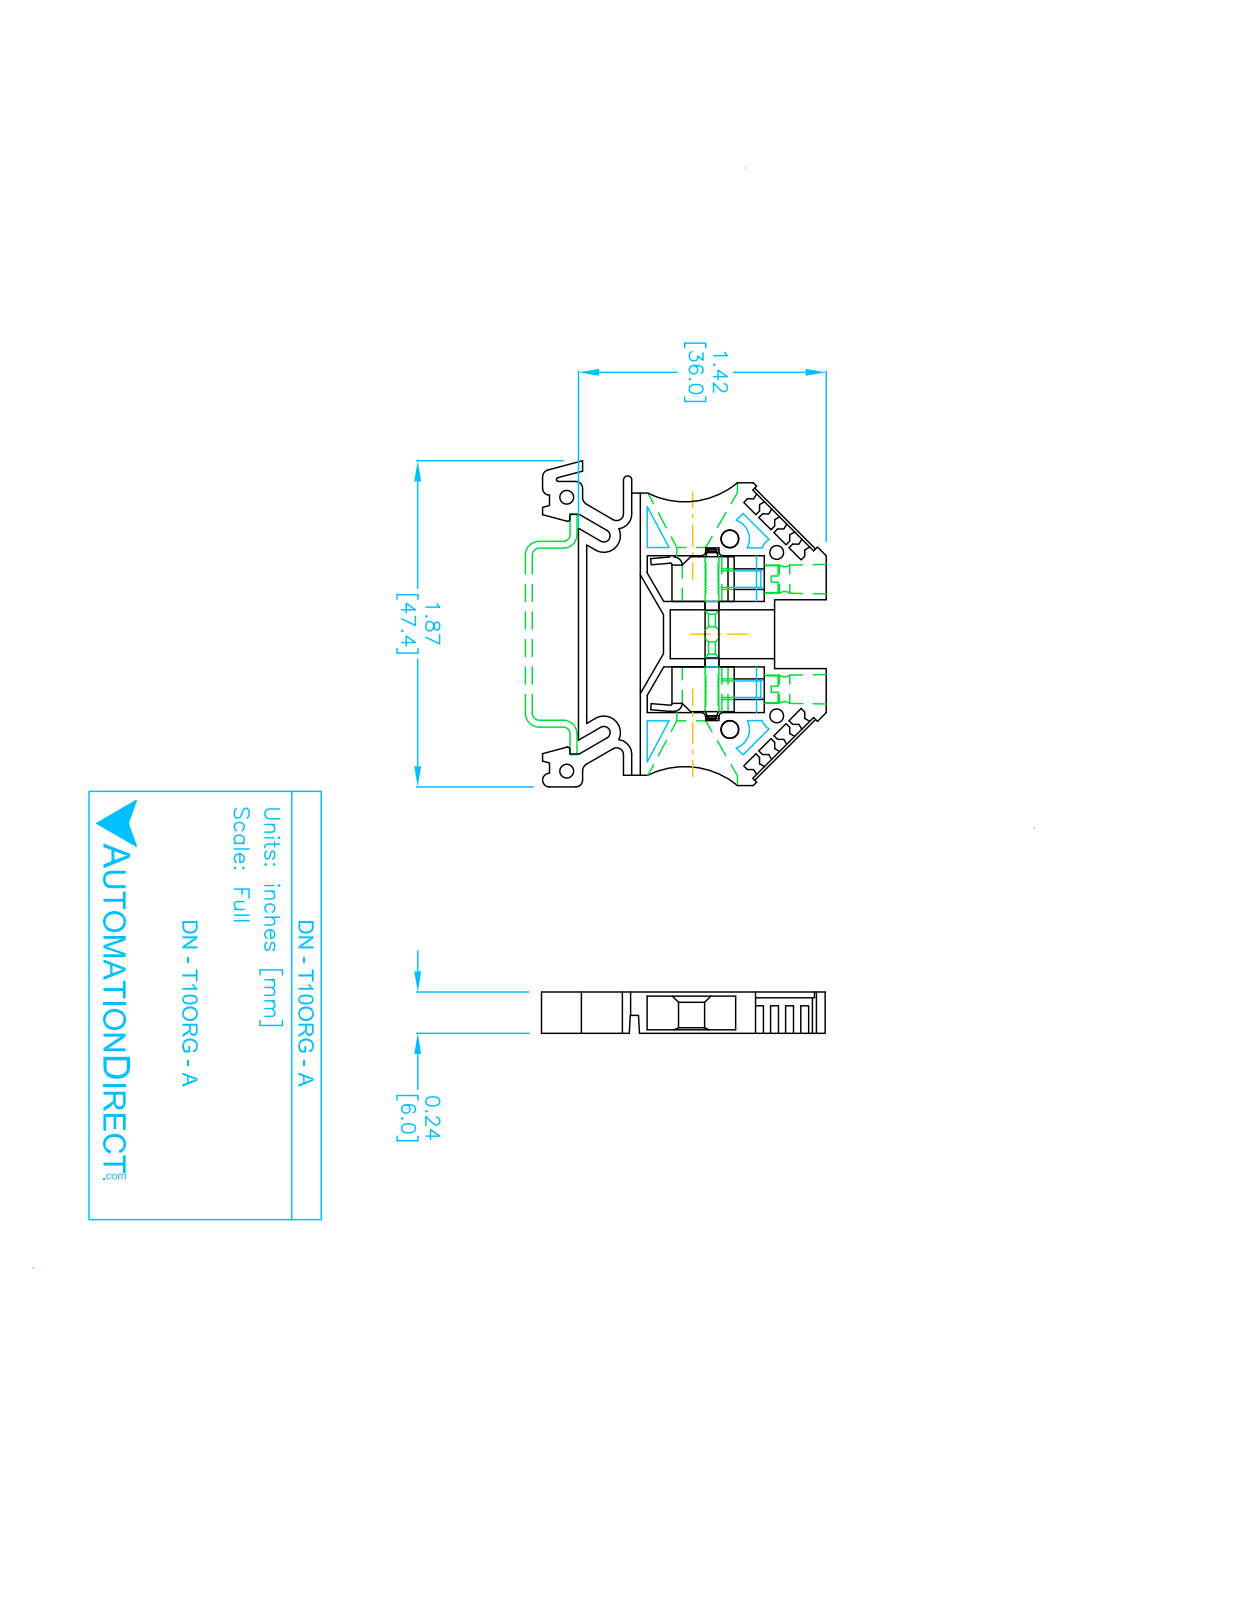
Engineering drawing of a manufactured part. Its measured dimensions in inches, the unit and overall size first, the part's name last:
Units: inches
Overall size (bounding box): 1.866 × 1.622 × 0.236
Round holes (diameter × count): ⌀0.079 ×2, ⌀0.172 ×2
Partial cylindrical surfaces — rounded edges, fillets, slot ends (radius × count): R0.039 ×7, R0.012 ×2, R0.035 ×2, R0.047 ×2, R0.087 ×2, R0.094 ×2, R0.472 ×2, R0.011 ×1
Main face-to-face distances: 0.228, 0.236, 0.142, 0.094, 0.047, 0.087, 0.134, 0.354, 0.071, 0.307
Hole centre spacings: 0.63, 1.567
Volume: 0.381 in³ · Surface area: 7.683 in²
Bodies: 1 solid, 181 faces (141 planar, 40 cylindrical, 0 other)
Part name (STEP PRODUCT): DN-T10ORG-A
STEP written by: SolidWorks 2017 (AUTOMOTIVE_DESIGN)
